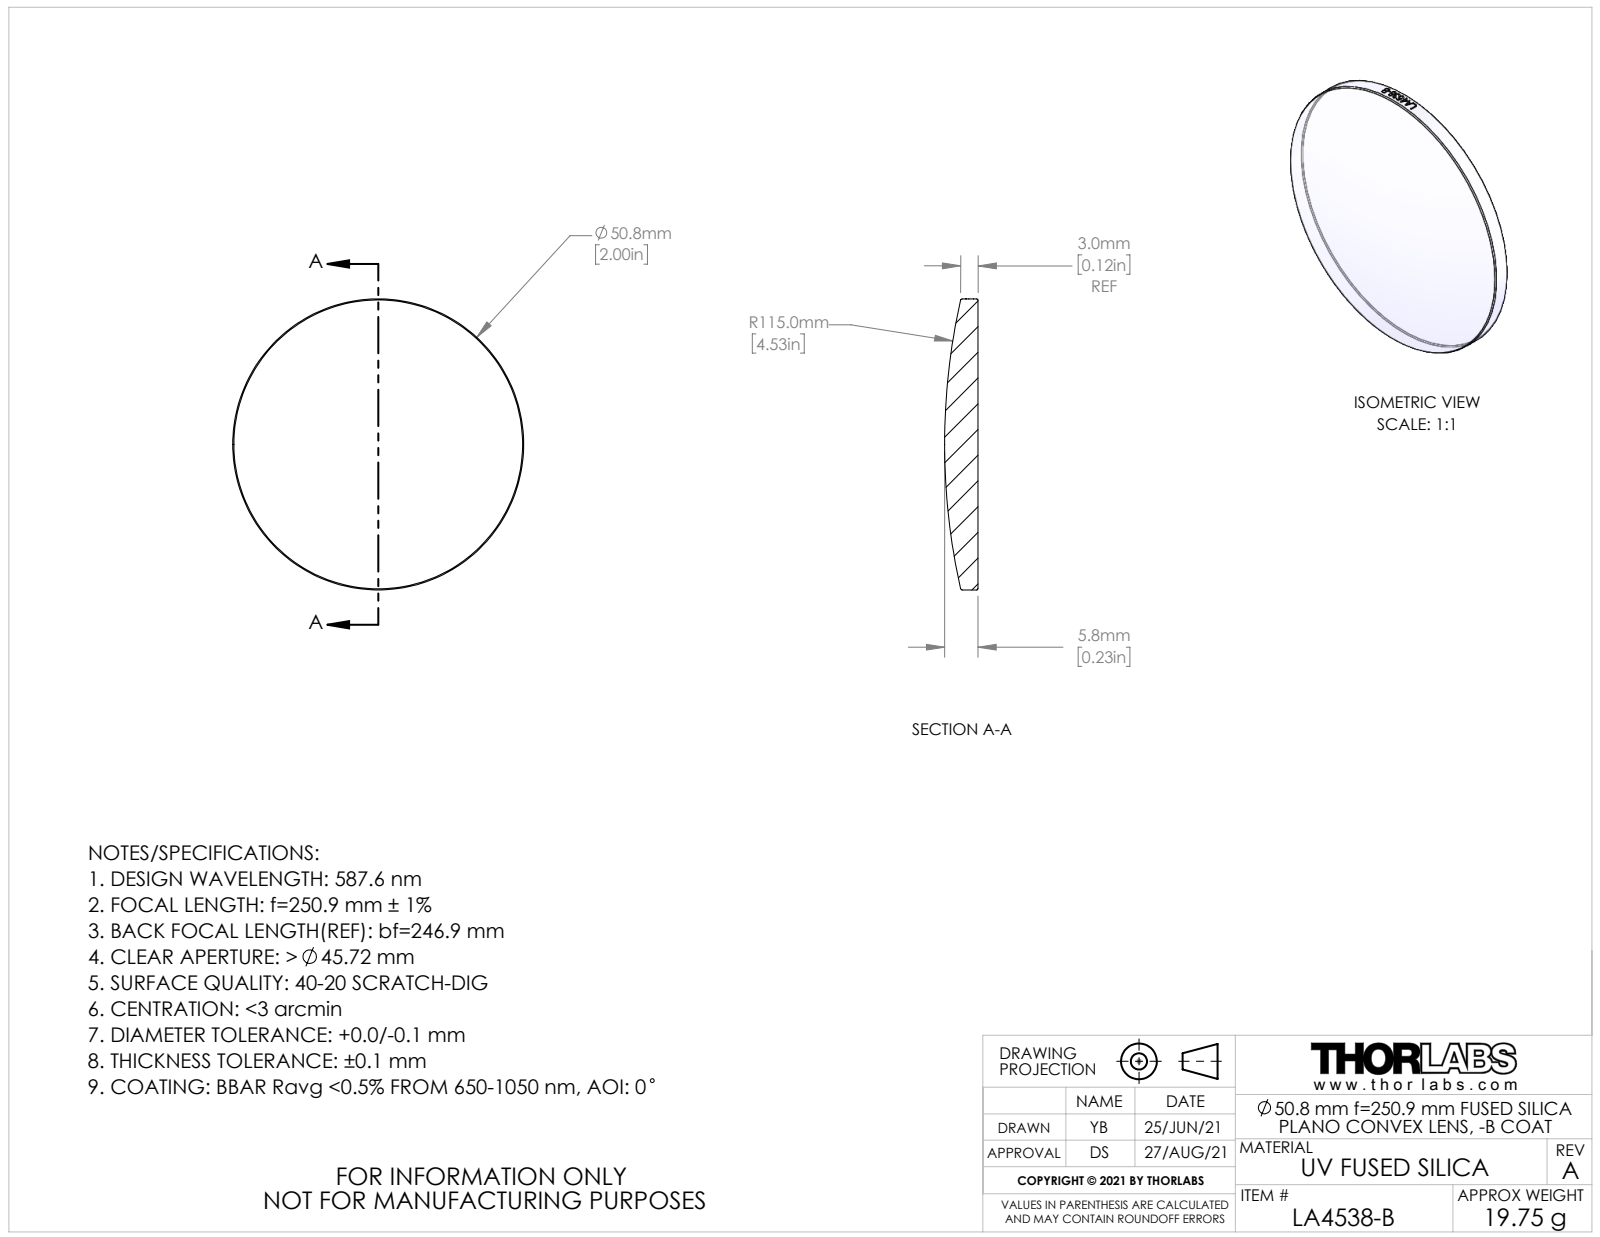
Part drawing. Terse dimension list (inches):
name: CTN017907-E0W
written by: SolidWorks 2018 (AUTOMOTIVE_DESIGN)
unit: in
bodies: 1 solid, 23 faces (1 planar, 16 cylindrical, 6 other)
size: 2 × 2 × 0.23
volume: 0.547 in³; area: 7.014 in²
bosses: 1× ⌀2
